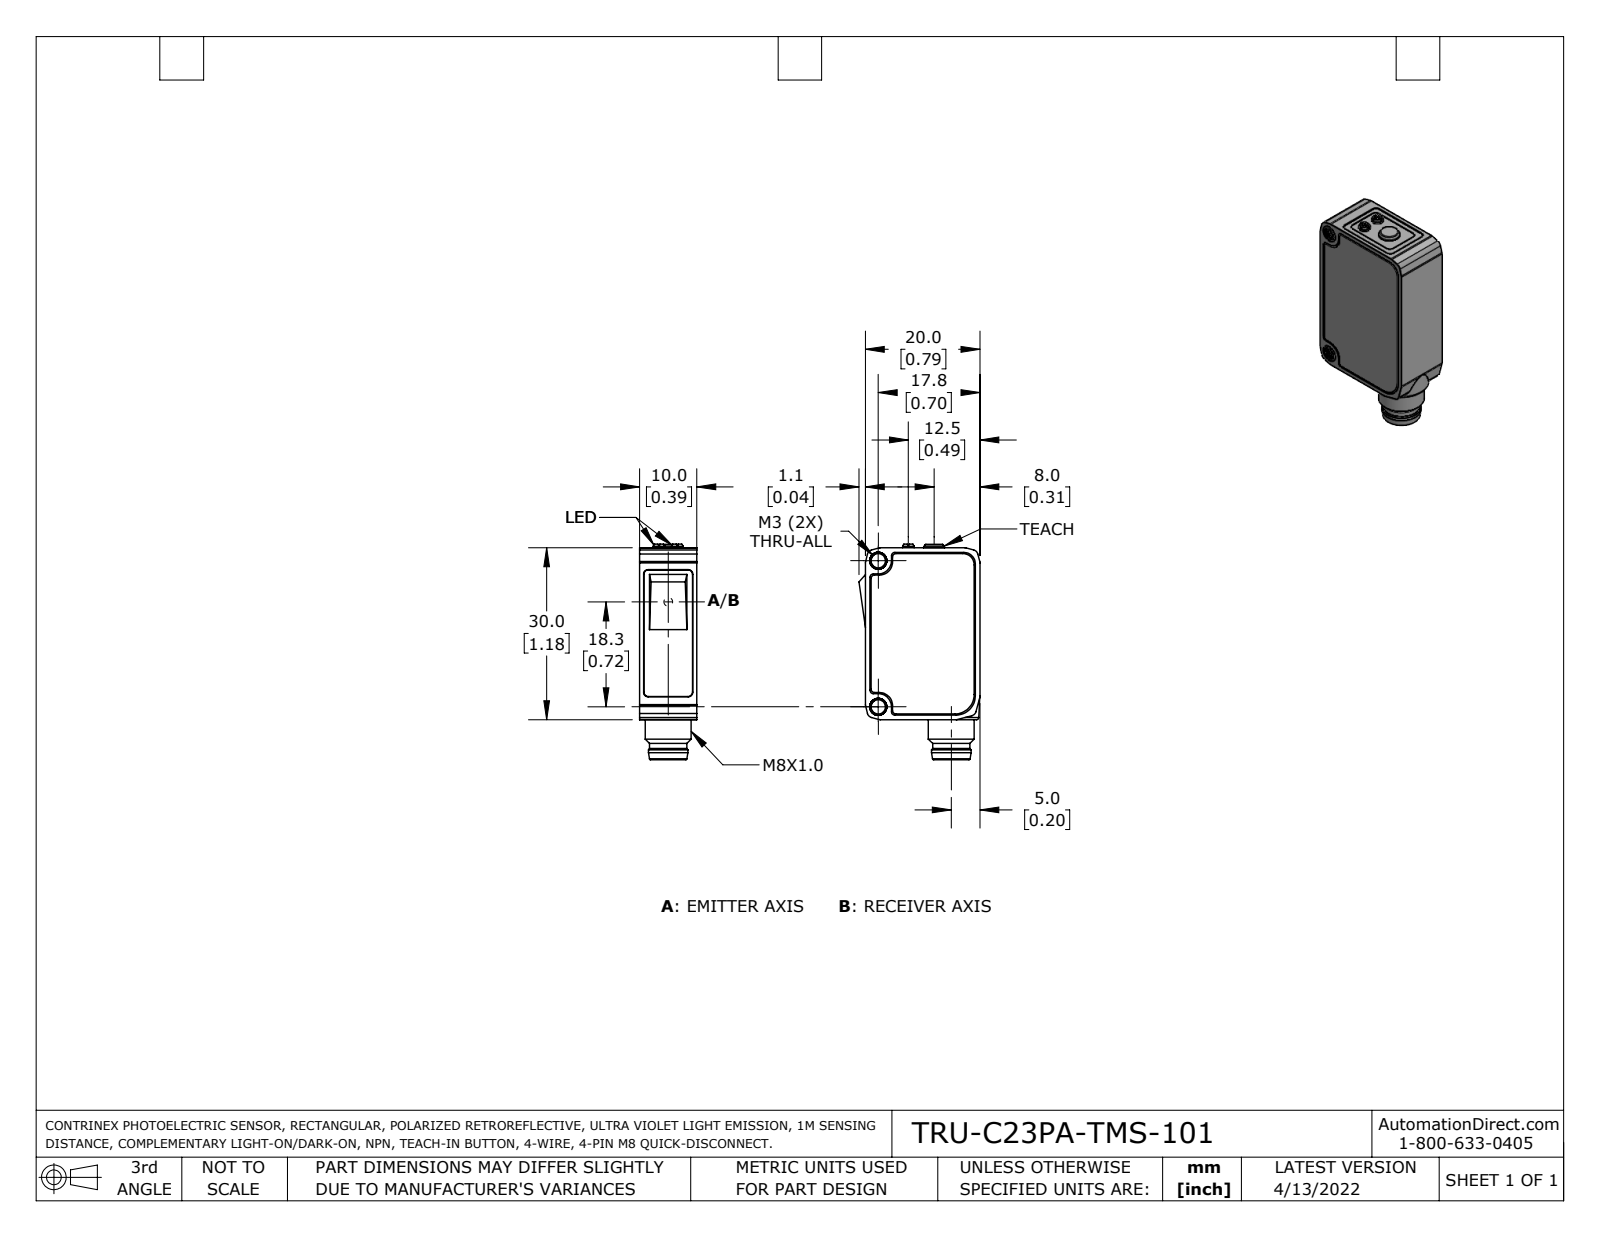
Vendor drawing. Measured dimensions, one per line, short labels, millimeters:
name: TRU-C23PA-TMS-101
written by: SolidWorks 2021 (AUTOMOTIVE_DESIGN)
unit: mm
bodies: 1 solid, 283 faces (92 planar, 137 cylindrical, 54 other)
size: 37.6 × 21.1 × 10
volume: 6 000 mm³; area: 2 830 mm²
holes: 2× ⌀2.5, 2× ⌀3.6, 1× ⌀5.8
bosses: 4× ⌀1, 2× ⌀2, 1× ⌀8, 1× ⌀6.9, 1× ⌀6.5, 1× ⌀3.7
rounds: 20× R0.8, 11× R1, 8× R0.6, 4× R2.3, 2× R2, 2× R3.4
face distances: 10, 19.9, 20, 29.9, 30, 0.7, 29.9, 0.8, 0.8, 1
hole spacings: 25.5
